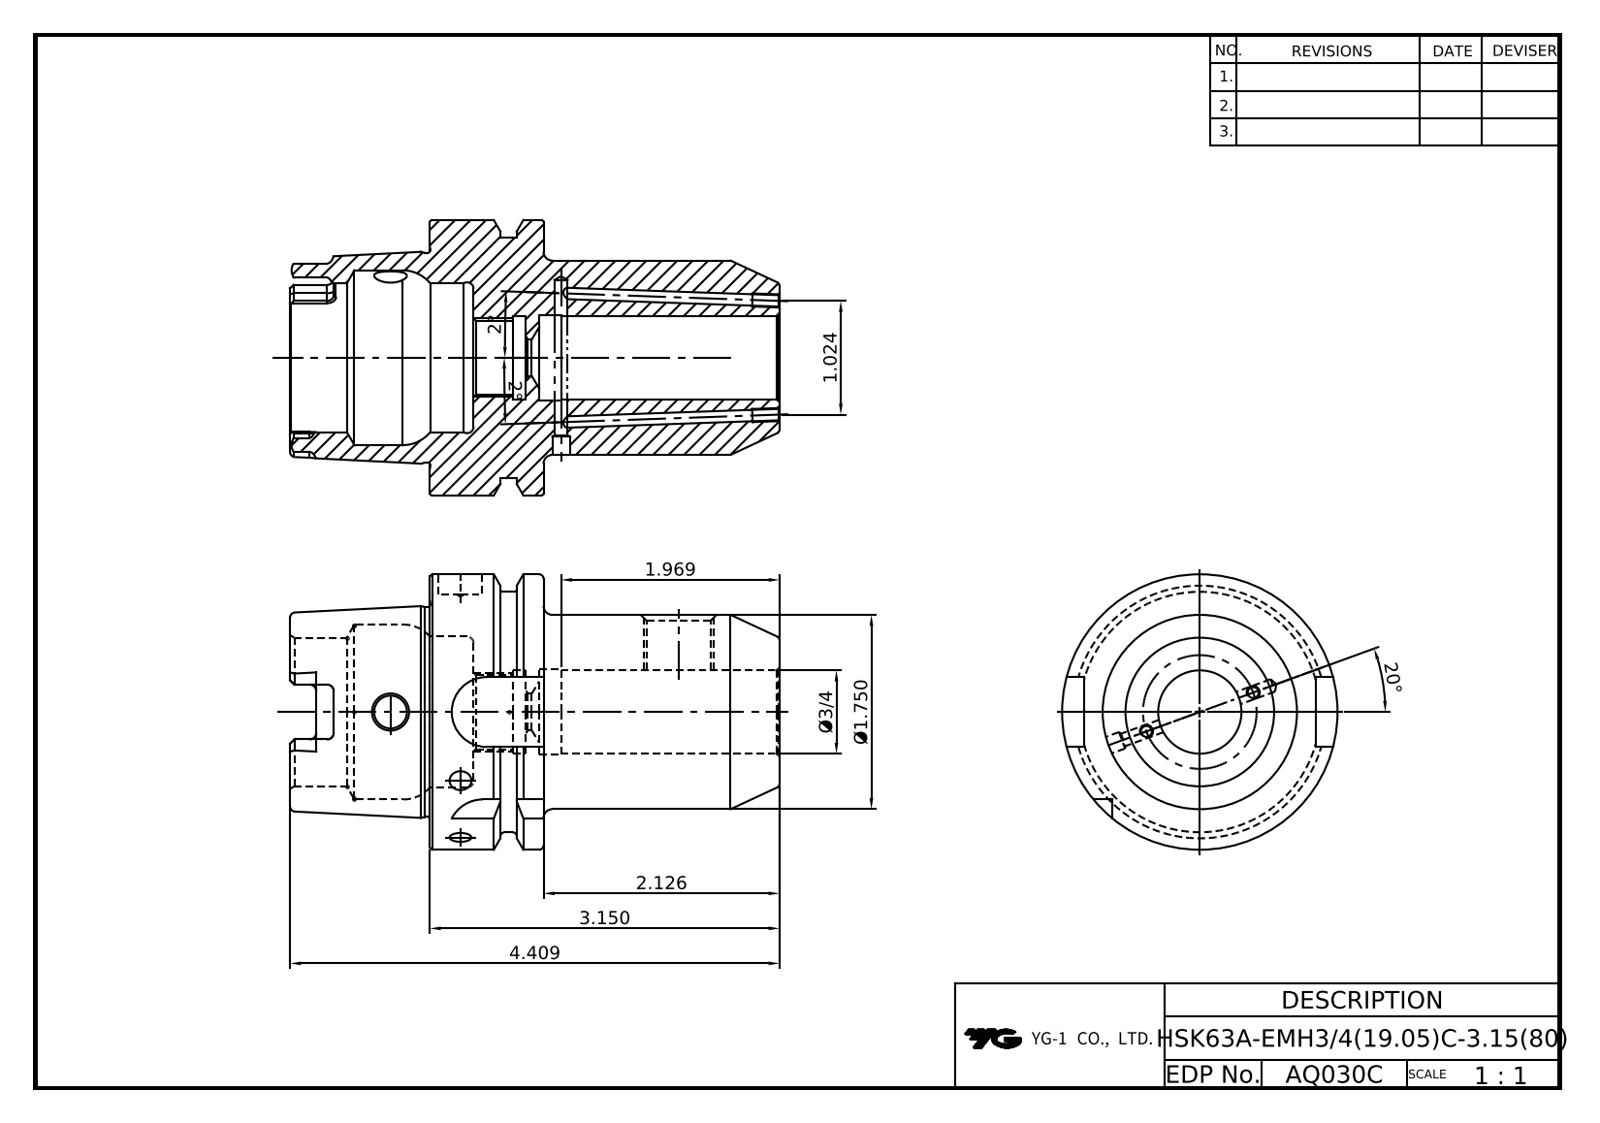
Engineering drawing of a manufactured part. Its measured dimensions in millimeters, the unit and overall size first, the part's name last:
Units: millimetres
Overall size (bounding box): 112 × 63 × 63
Round holes (diameter × count): ⌀2.46 ×2, ⌀7.5 ×1, ⌀8.4 ×1, ⌀10 ×1, ⌀14.35 ×1, ⌀16.92 ×1, ⌀19 ×1, ⌀19.05 ×1, ⌀20.25 ×1, ⌀34 ×1, ⌀40 ×1
Round bosses / shafts (diameter × count): ⌀63 ×1, ⌀55 ×1, ⌀48.04 ×1, ⌀44.45 ×1
Partial cylindrical surfaces — rounded edges, fillets, slot ends (radius × count): R1.5 ×6, R2.88 ×4, R8 ×4
Main face-to-face distances: 26, 54, 10, 80, 58, 16, 70, 32, 42, 112
Hole centre spacings: 49.9
Volume: 143 038 mm³ · Surface area: 33 490 mm²
Bodies: 1 solid, 118 faces (42 planar, 36 cylindrical, 40 other)
Part name (STEP PRODUCT): HSK63A-EMH19.05C-3.15
STEP written by: Autodesk Inventor 2024 (AUTOMOTIVE_DESIGN)
